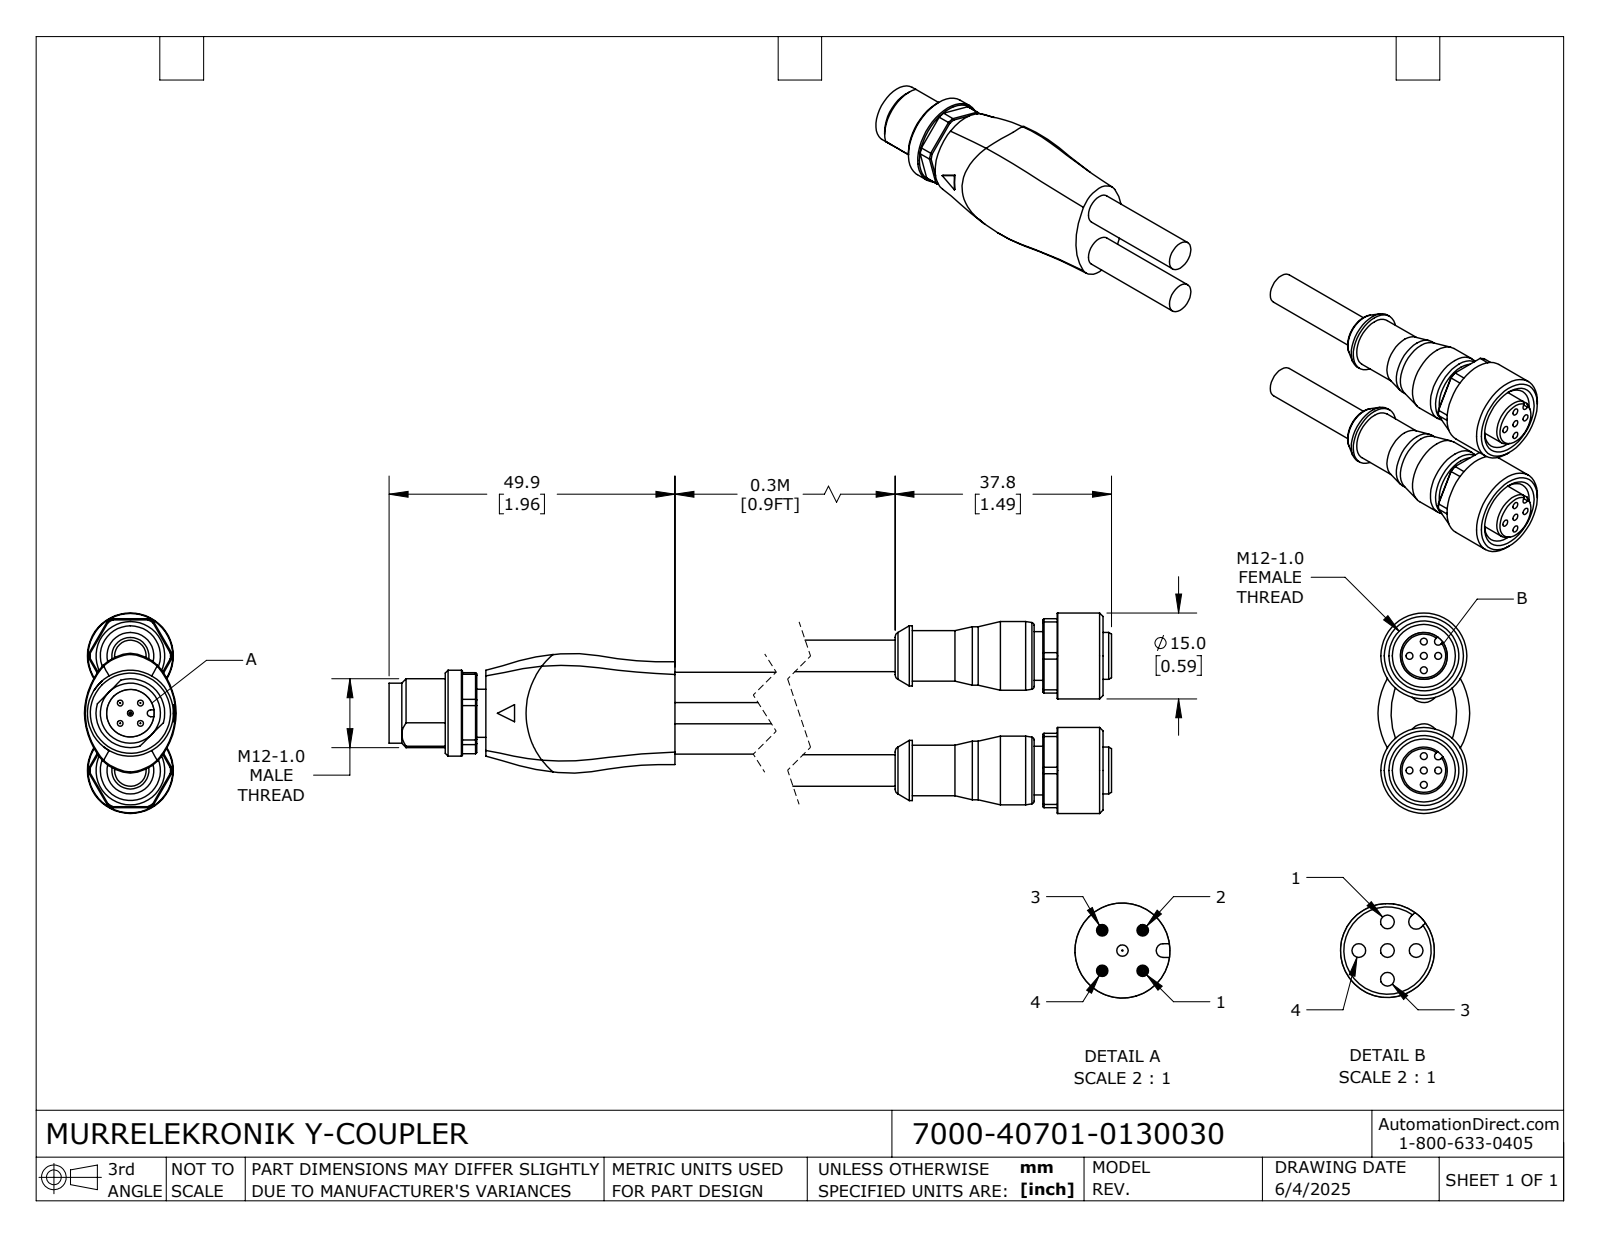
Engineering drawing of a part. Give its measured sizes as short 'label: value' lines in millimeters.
name: 7000-40701-0130030_FEMALE; 7000-40701-0130030_MALE; 7000-40701-0130030
written by: SolidWorks 2024 (CONFIG_CONTROL_DESIGN)
unit: mm
bodies: 3 solids, 283 faces (93 planar, 103 cylindrical, 87 other)
size: 152.7 × 35 × 16.01
volume: 17 544 mm³; area: 9 297 mm²
holes: 10× ⌀1.2, 2× ⌀11, 1× ⌀8.3
bosses: 5× ⌀1, 3× ⌀15, 3× ⌀10.5, 2× ⌀12, 2× ⌀10.2, 2× ⌀8.8, 2× ⌀8.5, 2× ⌀8.2
rounds: 3× R7.2, 2× R0.65, 1× R0.6, 1× R6
face distances: 3, 12, 33, 1.5, 13, 123.8, 90.8, 134.3, 10.5, 8
hole spacings: 2.5, 3.54, 20, 5, 10.31, 17.68, 20.16, 22.64
